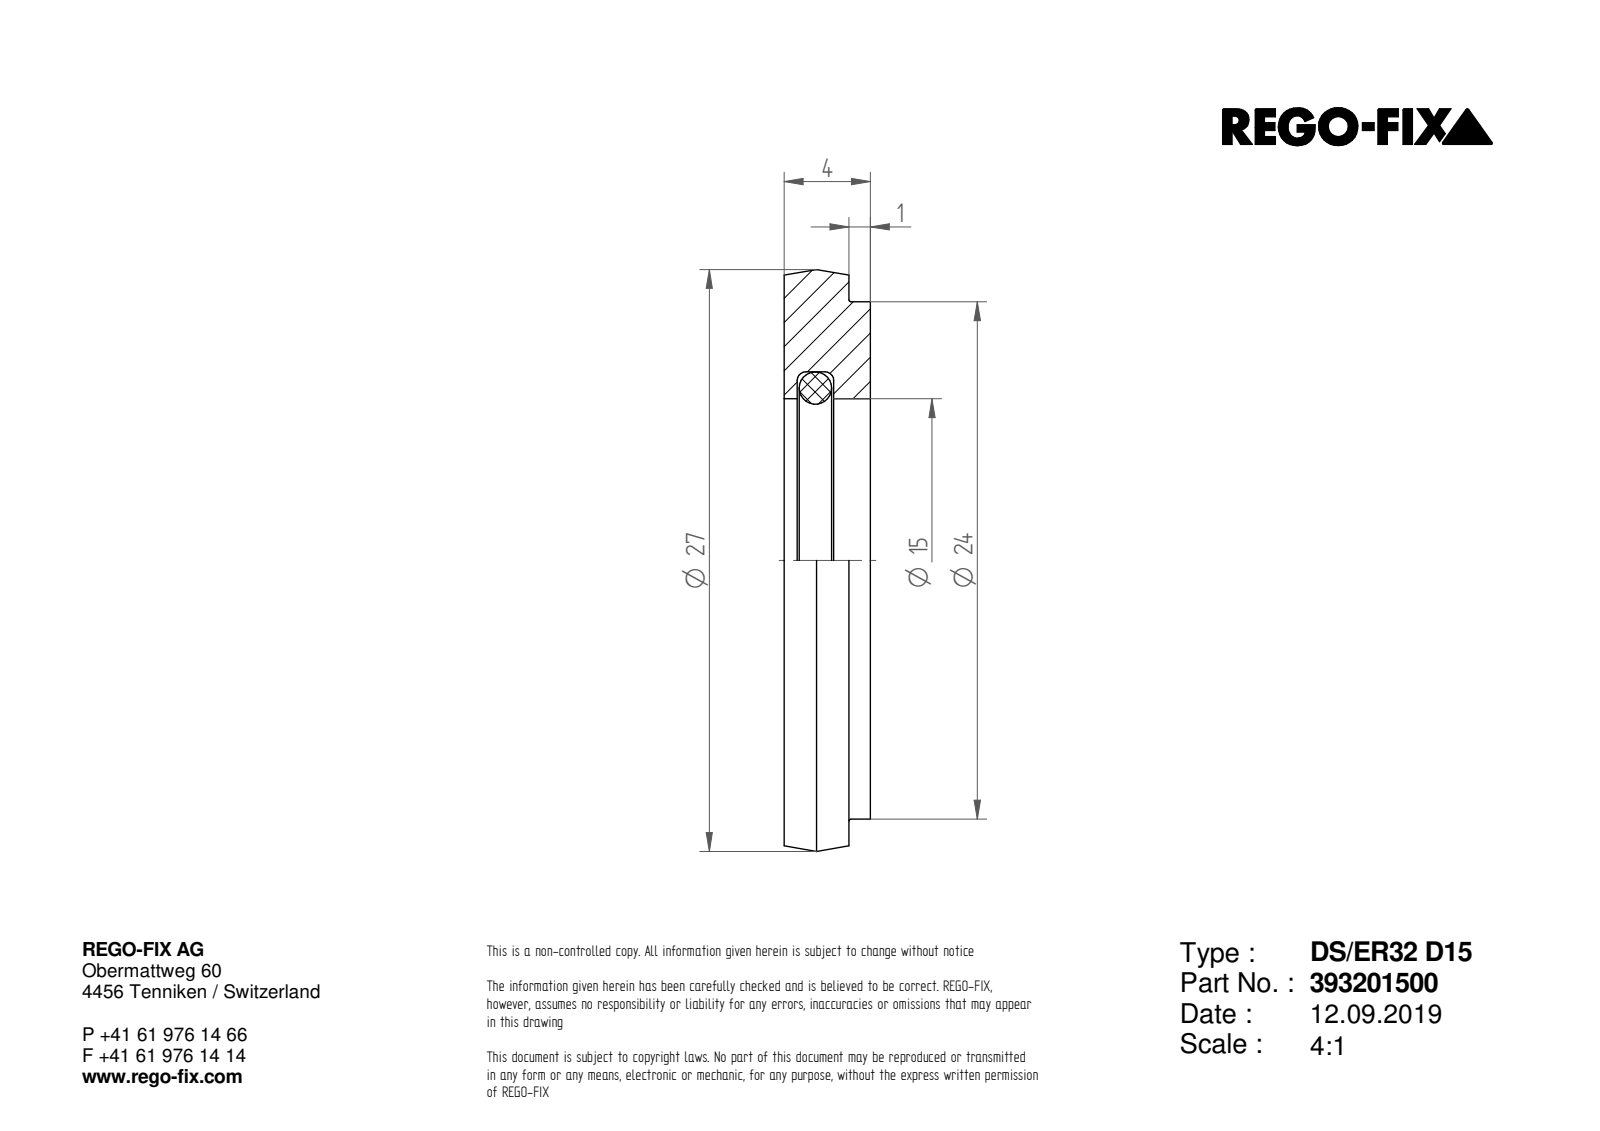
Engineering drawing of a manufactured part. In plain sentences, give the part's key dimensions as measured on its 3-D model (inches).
The part is named "NOCUT". Its 3-D file was written by "SIEMENS PLM Software Solid Edge ST10 (AUTOMOTIVE_DESIGN)". It is 1 solid with 7 faces: 3 planar, 3 cylindrical and 1 other. Overall it measures 1.063 by 1.063 by 0.157 inches. Its volume is 0.089 cubic inches and its surface area 2.026 square inches. Round holes: 1 of diameter 0.591. Round bosses or shafts: 1 of diameter 1.063, 1 of diameter 0.945. The main face-to-face distances are 0.157, 0.039, 0.118.
